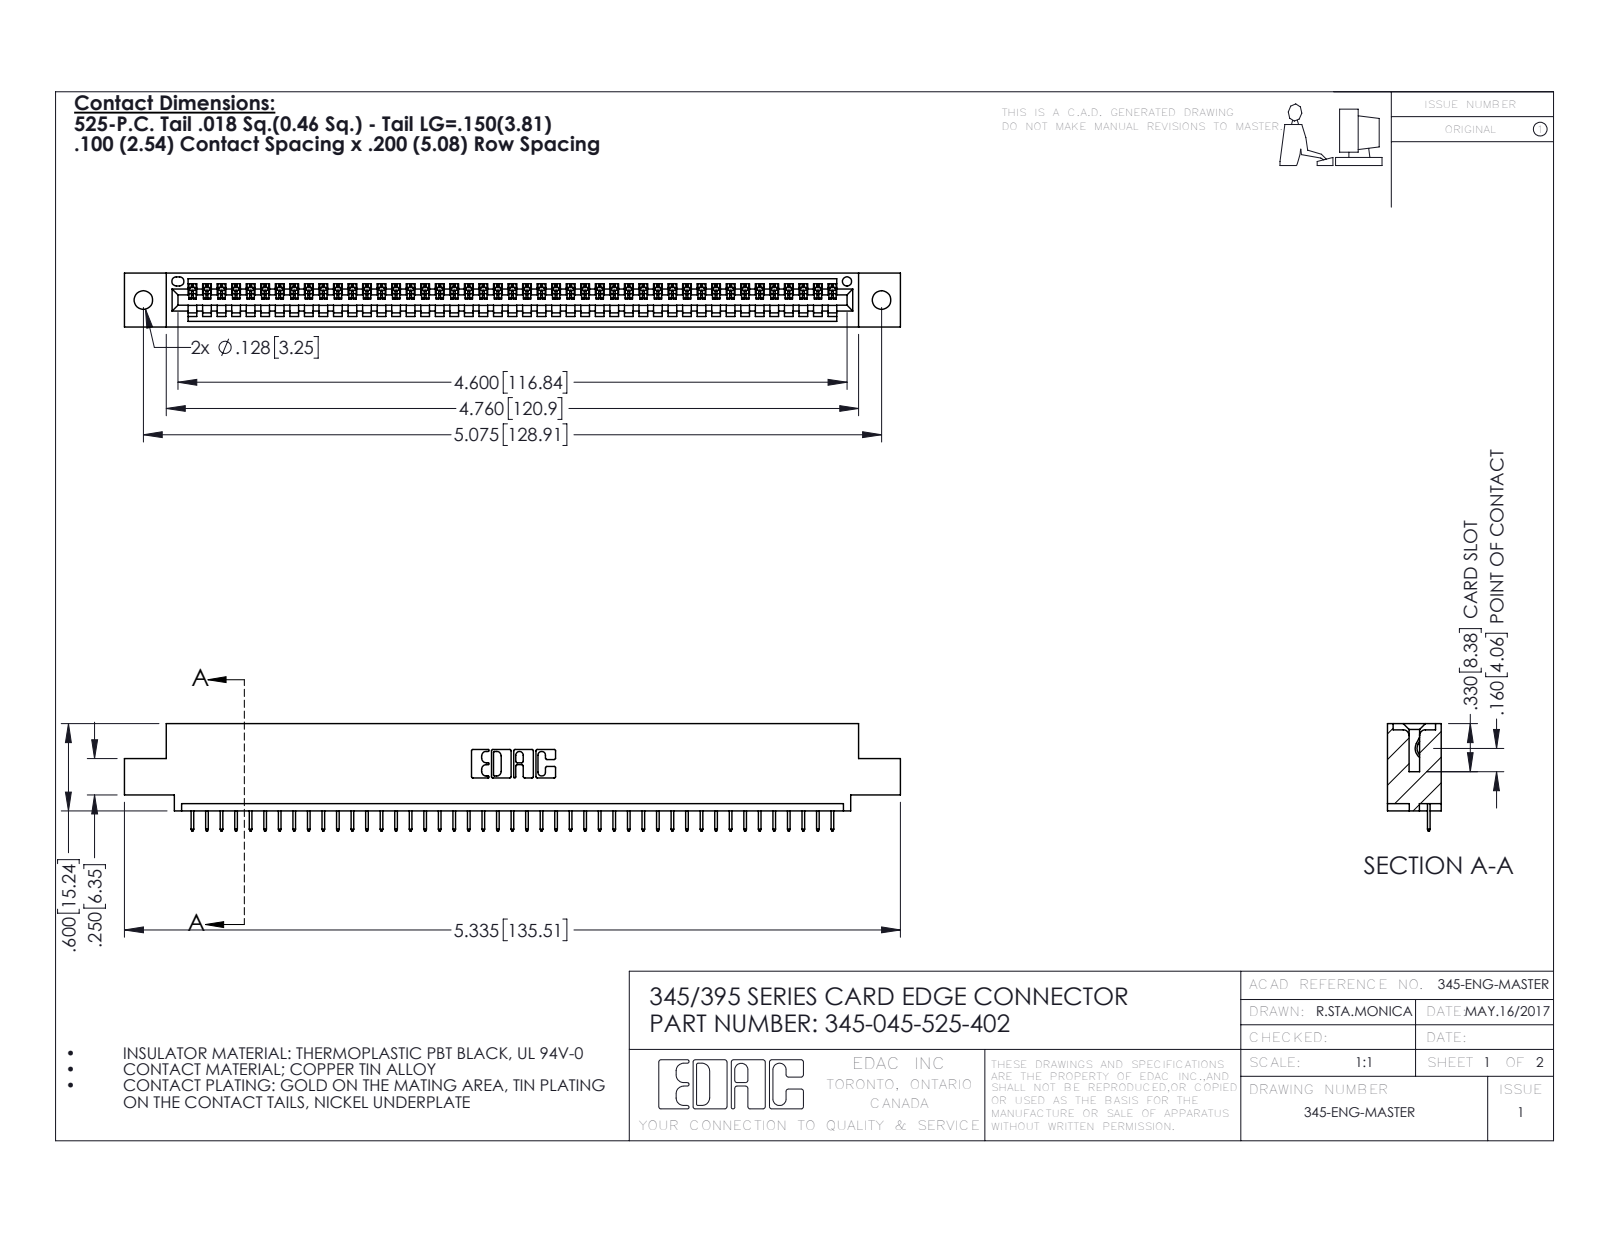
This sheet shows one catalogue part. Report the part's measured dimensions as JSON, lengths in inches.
{"part_name": "345-045-525-402; 345 Part_0.110 Offset - 0.128 Dia; 345-292-001_345-293-125", "step_written_by": "SolidWorks 2020 (CONFIG_CONTROL_DESIGN)", "units": "inches", "bodies": {"solids": 46, "faces": 2920, "planar": 2154, "cylindrical": 766, "other": 0}, "overall_size": [5.335, 0.737, 0.37], "volume_in3": 0.769, "surface_area_in2": 24.78, "round_holes": [[0.128, 2], [0.064, 1]], "partial_cylinders_radius": [[0.006, 90], [0.01, 22], [0.007, 6], [0.031, 6], [0.026, 3], [0.031, 2], [0.04, 2], [0.014, 1]], "face_to_face_distances": [0.072, 0.298, 0.37, 0.2, 0.098, 0.272, 0.025, 0.225, 0.072, 0.149], "hole_center_spacings": [0.27, 4.839, 5.075]}
